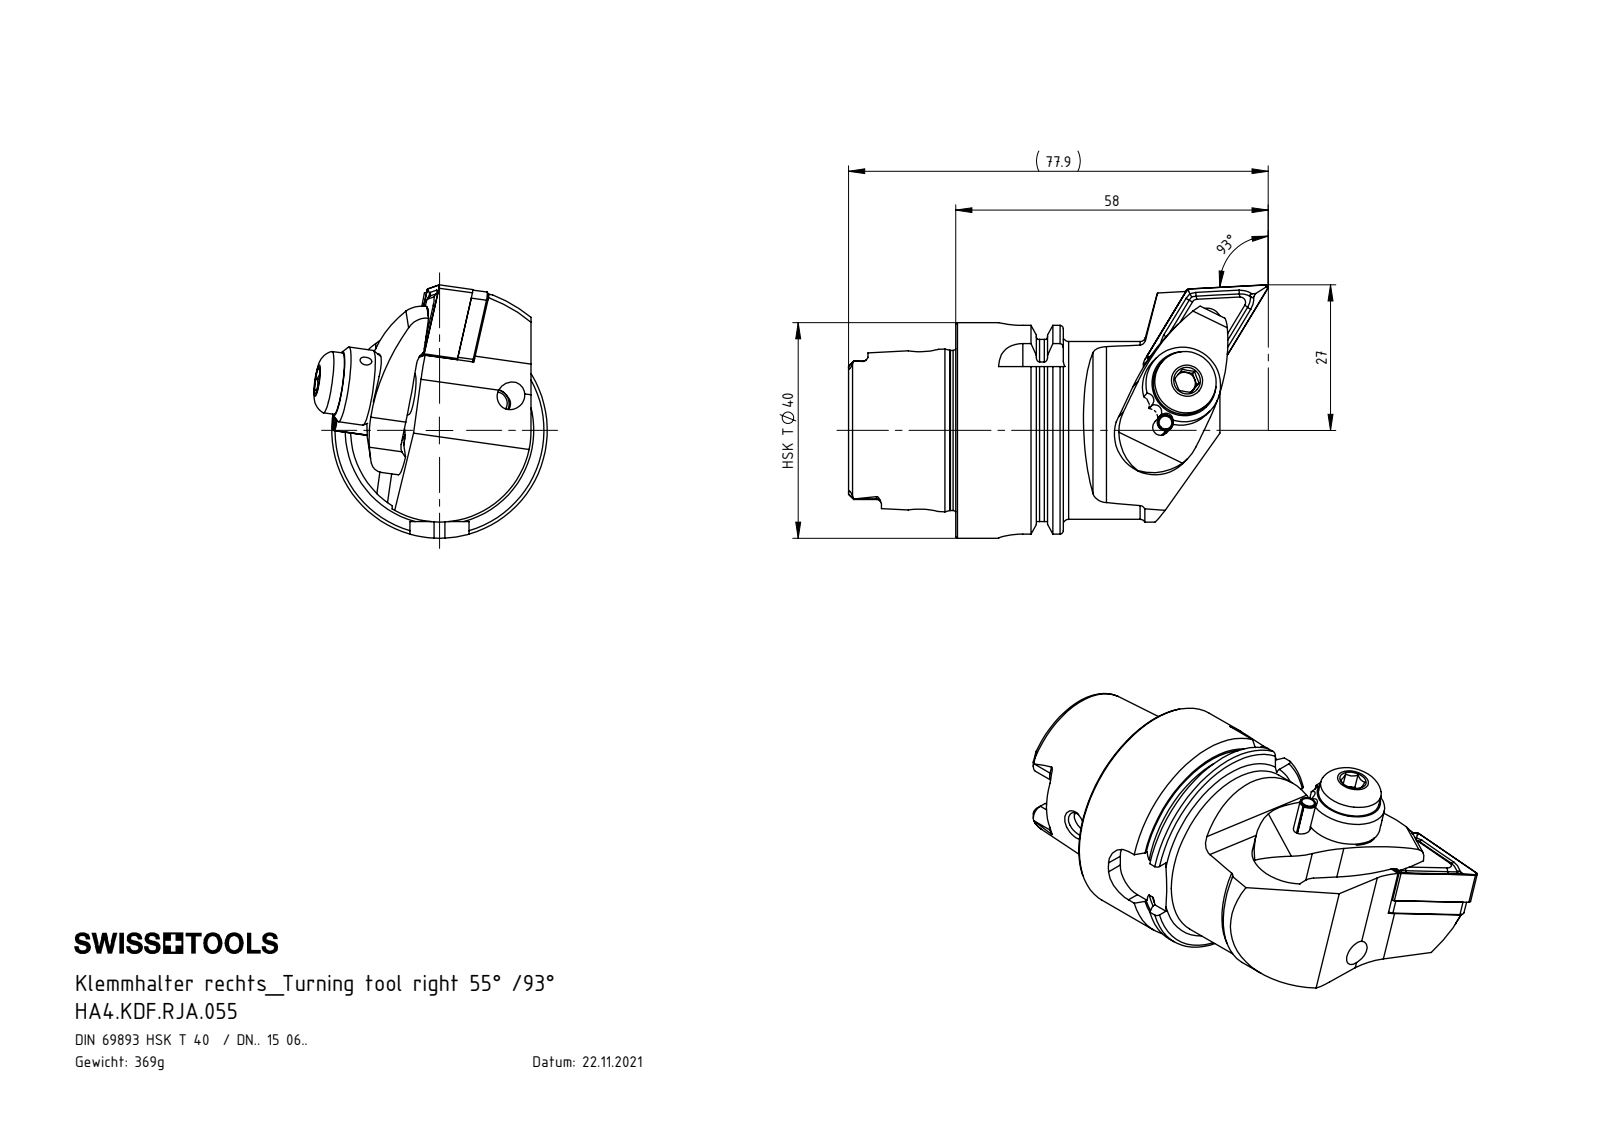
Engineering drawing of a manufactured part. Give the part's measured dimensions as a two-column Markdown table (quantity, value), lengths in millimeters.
| quantity | value |
| --- | --- |
| part name | WCC-ER3.102.024_C; ISO 13337 - 3 x 12_Spring Pin ISO 13337 - 3 x 16 - St; DNMG150604; KVT_MB_600_050 (+7 more) |
| STEP written by | SolidWorks 2017 (AUTOMOTIVE_DESIGN) |
| units | millimeters |
| bodies | 11 solids, 467 faces (125 planar, 154 cylindrical, 188 other) |
| overall size | 77.9 × 47 × 43.32 |
| volume | 47 999 mm³ |
| surface area | 19 189 mm² |
| round holes (diameter × count) | 2 × 3, 5 × 3, 4.2 × 2, 7 × 2, 2.4 × 1, 3 × 1, 4 × 1, 4.6 × 1, 5.16 × 1, 6.2 × 1, 6.4 × 1, 8.5 × 1 |
| round bosses / shafts (diameter × count) | 5 × 2, 3 × 2, 40 × 1, 34.75 × 1, 33 × 1, 29.71 × 1, 14 × 1, 11.5 × 1 |
| partial cylindrical surfaces (radius × count) | 0.39 × 6, 0.9 × 6, 0.4 × 4, 1 × 4, 4.5 × 4, 0.69 × 3, 0.69 × 3, 1.5 × 3 |
| main face-to-face distances | 12.7, 6.02, 12.31, 7.95, 1.32, 7.34, 12, 9.21, 19.95, 3.19 |
| hole center spacings | 15, 23, 8, 8.01, 8.2, 8.21, 14.79, 14.8 |
